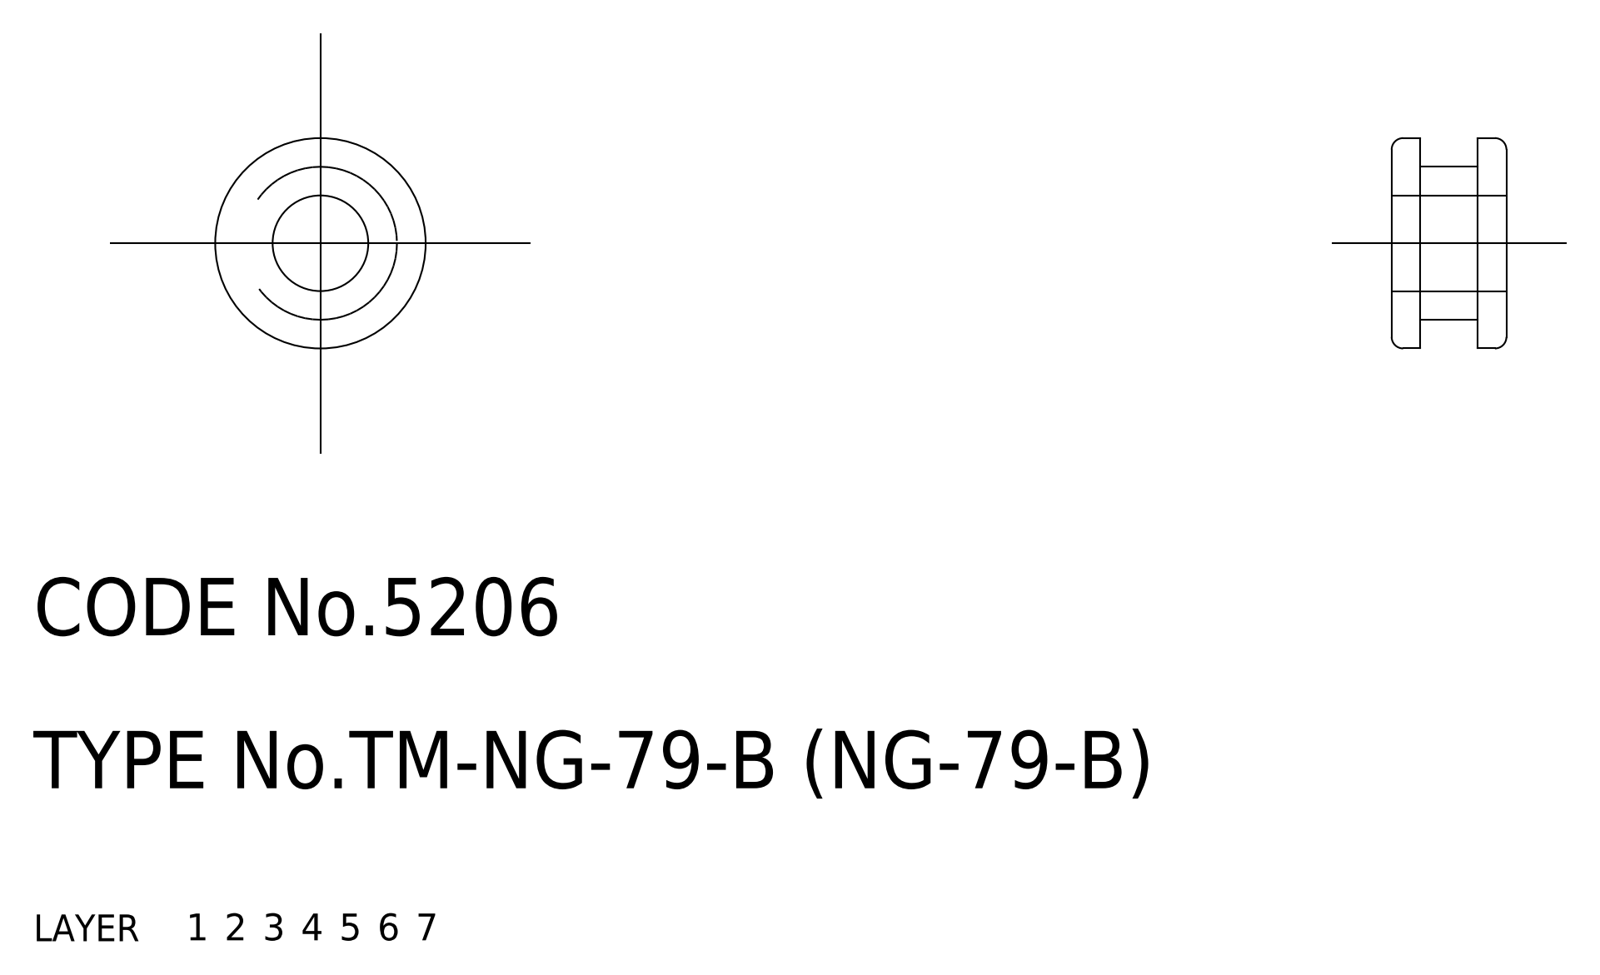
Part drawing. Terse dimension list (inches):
name: grommet
written by: CADfix (AUTOMOTIVE_DESIGN)
unit: in
bodies: 1 solid, 16 faces (0 planar, 0 cylindrical, 16 other)
size: 0.433 × 0.433 × 0.236
volume: 0.019 in³; area: 0.769 in²
